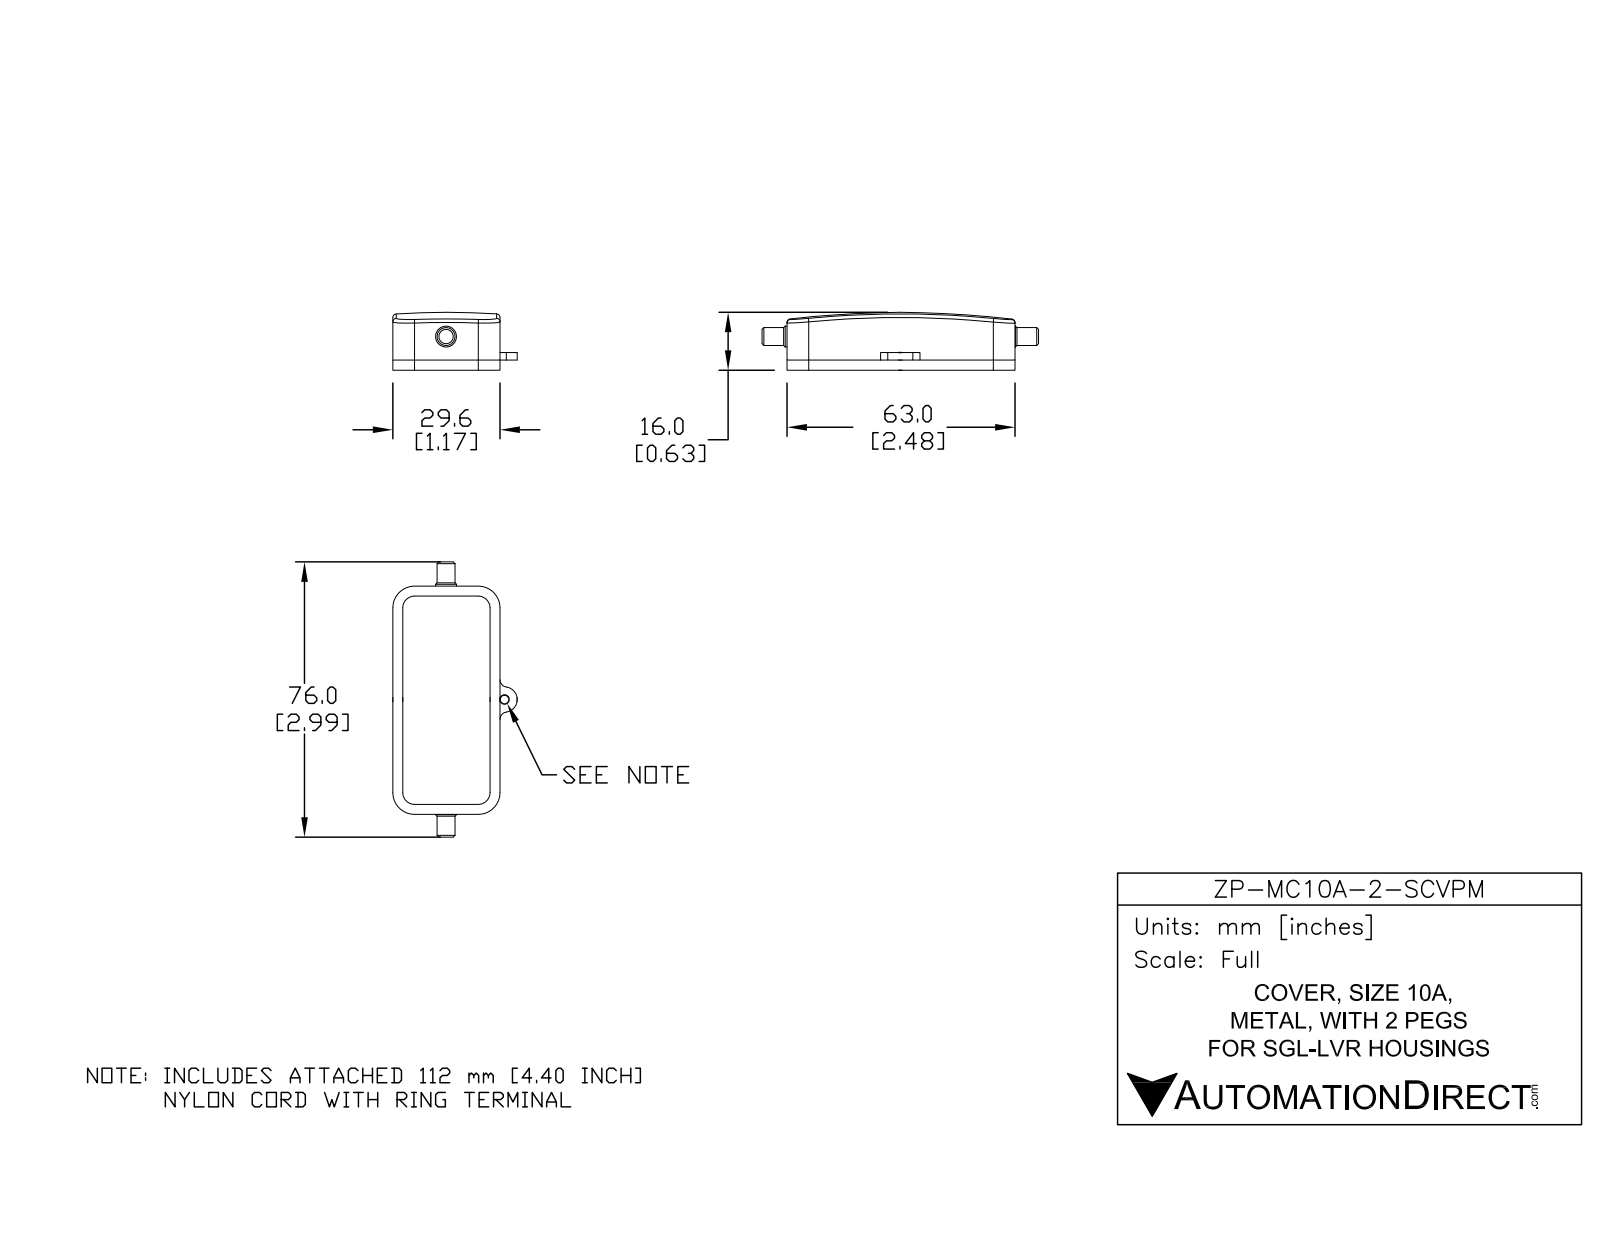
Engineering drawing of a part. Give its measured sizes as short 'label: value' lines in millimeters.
name: ZP-MC10A-2-SCVPM
written by: SolidWorks 2014 (AUTOMOTIVE_DESIGN)
unit: mm
bodies: 4 solids, 104 faces (40 planar, 40 cylindrical, 24 other)
size: 146.44 × 76.38 × 62.3
volume: 11 033 mm³; area: 9 395 mm²
holes: 1× ⌀2.5, 1× ⌀4.1
bosses: 1× ⌀5.77, 1× ⌀4.95
rounds: 6× R6, 4× R0.45, 4× R3.25, 2× R0.6, 2× R2, 1× R3.5, 1× R3.92
face distances: 2.75, 26.85, 29.6, 24.1, 60.25, 63, 57.5, 32.15, 29.4, 28.1
